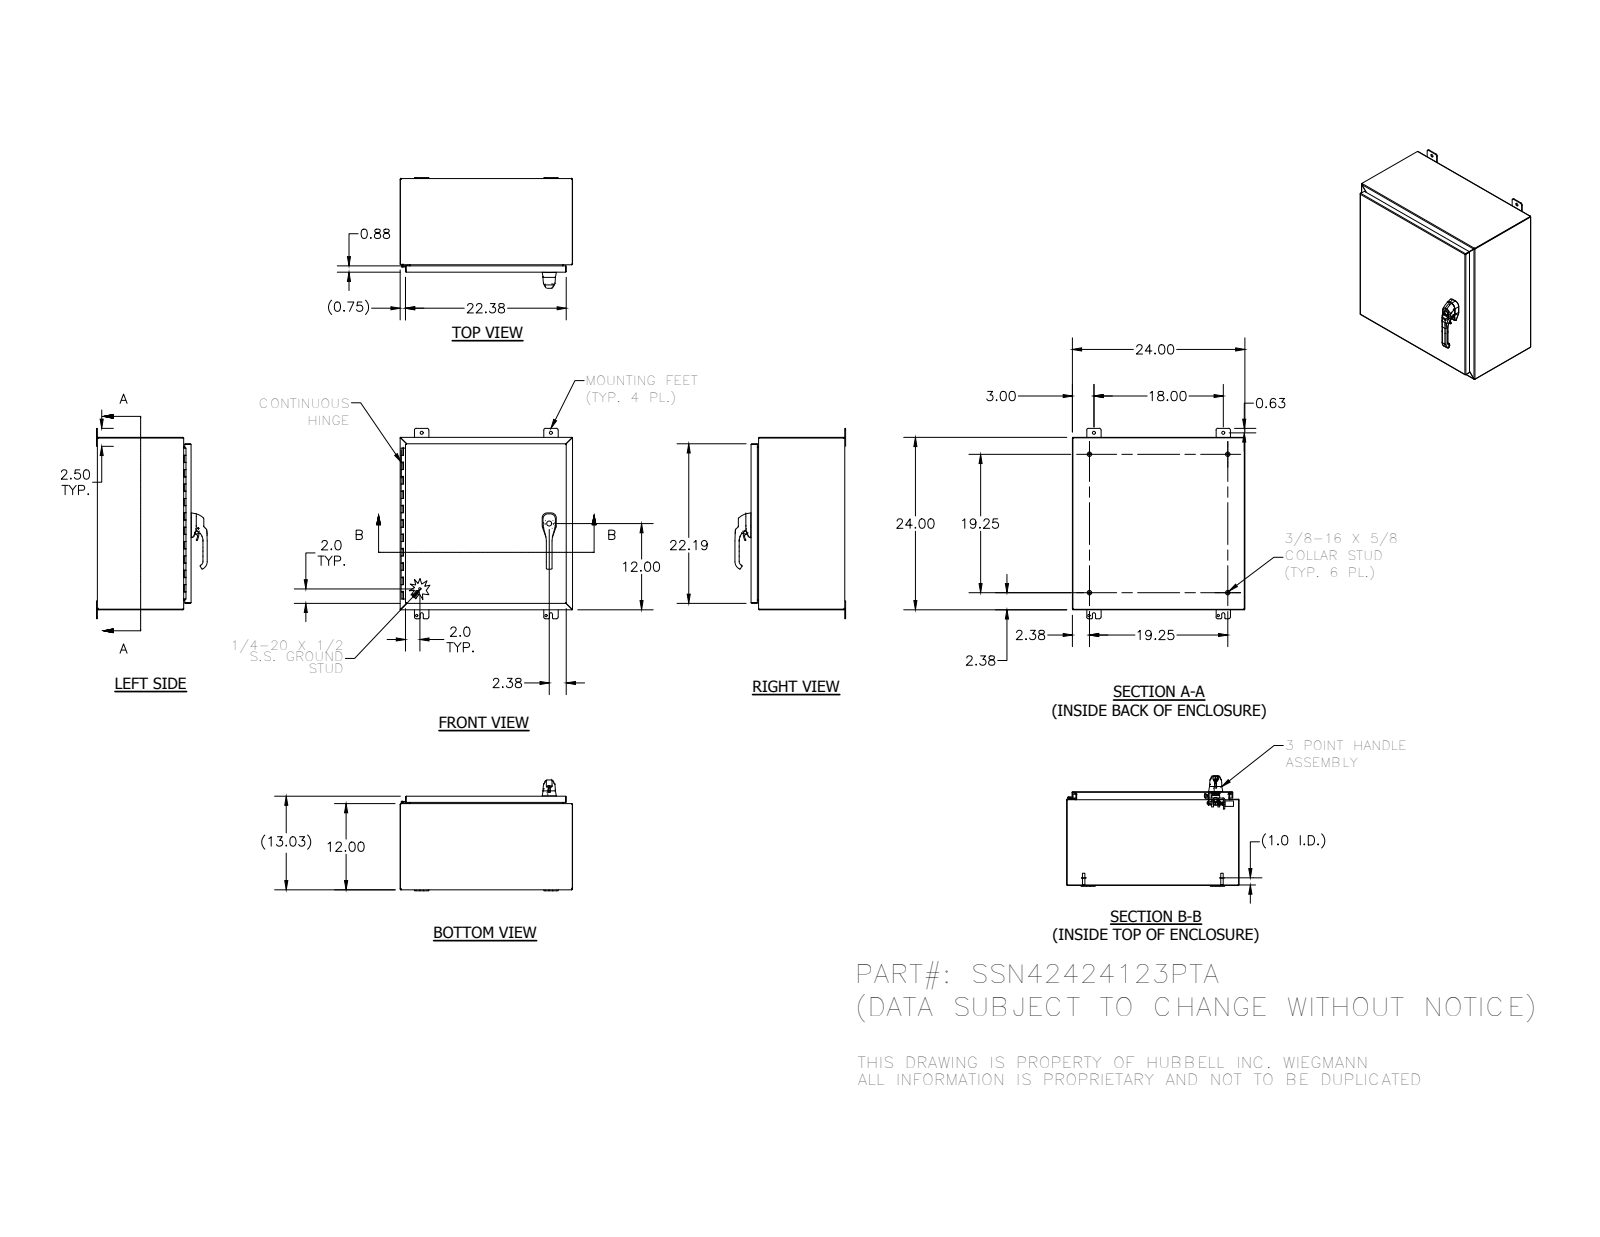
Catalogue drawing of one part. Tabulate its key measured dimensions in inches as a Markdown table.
| quantity | value |
| --- | --- |
| part name | LOCK-NUT_AF0; 7379-M6-8X25_AF0; SSN42424123PTABKP; D125B_10_5 (+8 more) |
| STEP written by | SolidWorks 2014 (AUTOMOTIVE_DESIGN) |
| units | inches |
| bodies | 56 solids, 3071 faces (1014 planar, 1270 cylindrical, 787 other) |
| overall size | 26.5 × 24 × 15.408 |
| volume | 212.4 in³ |
| surface area | 5 494 in² |
| round holes (diameter × count) | 0.262 × 8, 0.187 × 4, 0.313 × 4, 0.438 × 4, 0.213 × 3, 0.281 × 3, 0.241 × 2, 0.25 × 2, 0.252 × 2, 0.315 × 2, 0.4 × 2, 0.402 × 2 |
| round bosses / shafts (diameter × count) | 0.625 × 4, 0.33 × 4, 0.236 × 3, 1 × 2, 0.563 × 2, 0.533 × 2, 0.531 × 2, 0.5 × 2 |
| partial cylindrical surfaces (radius × count) | 0.02 × 172, 0.012 × 113, 0.125 × 26, 0.031 × 24, 0.019 × 21, 0.105 × 20, 0.25 × 20, 0.025 × 16 |
| main face-to-face distances | 0.074, 23.926, 12.959, 23.852, 24, 12.885, 13.033, 11.926, 1.033, 12 |
| hole center spacings | 0.38, 0.492, 0.76, 1.593, 18, 24, 30, 0.886 |
